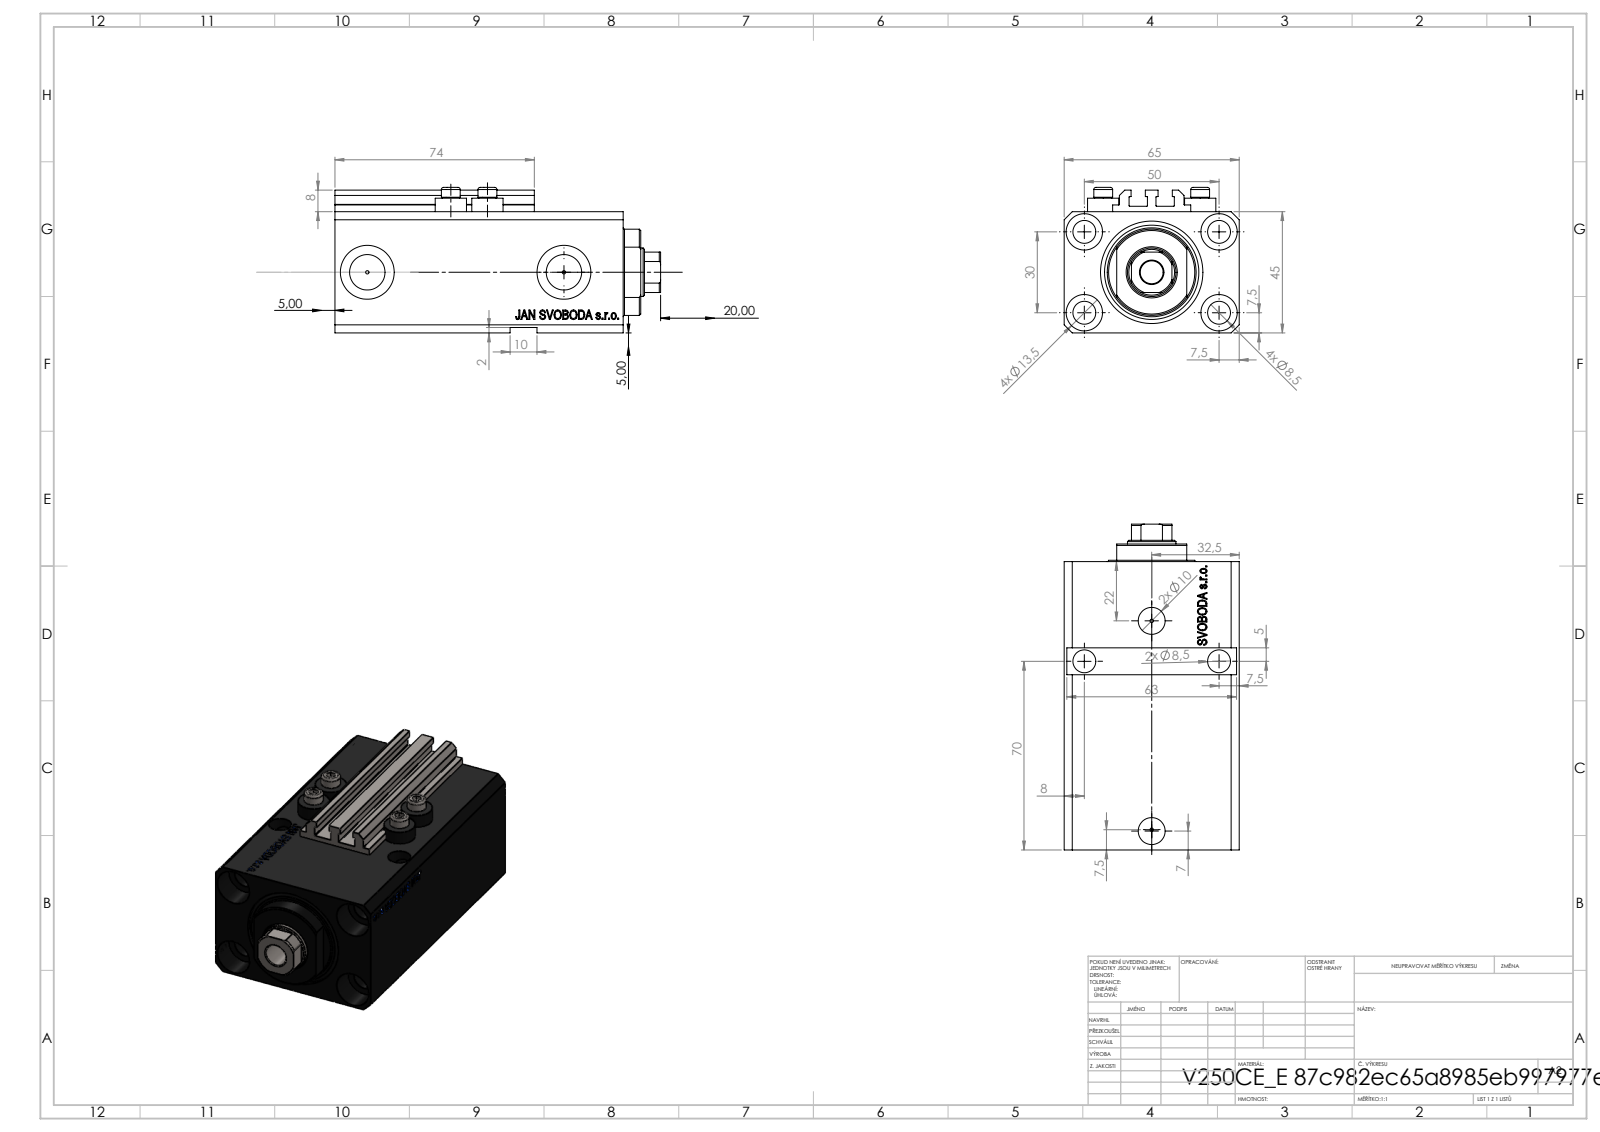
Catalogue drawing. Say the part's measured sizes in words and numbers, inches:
The part is named "V250CE_C_VCP; V250CE_E_Body; ALLEN BOLT V250CE; V250CE_VC_E". Its 3-D file was written by "SolidWorks 2019 (CONFIG_CONTROL_DESIGN)". It is 8 solids with 1087 faces: 511 planar, 146 cylindrical and 430 other. Overall it measures 4.764 by 2.559 by 2.126 inches. Its volume is 16.68 cubic inches and its surface area 119.2 square inches. Round holes: 9 of diameter 0.335, 4 of diameter 0.049, 4 of diameter 0.157, 4 of diameter 0.531, 2 of diameter 0.394, 2 of diameter 0.518, 2 of diameter 0.787, 1 of diameter 0.709, 1 of diameter 0.984, 1 of diameter 1.496. Round bosses or shafts: 4 of diameter 0.457, 4 of diameter 0.276. Partial cylindrical surfaces (rounded edges, fillets, slot ends): 10 of radius 0.008, 1 of radius 0.335, 1 of radius 0.63. The main face-to-face distances are 1.772, 2.559, 3.661, 0.079, 0.551, 1.85, 4.213, 0.098, 0.394, 0.807. The hole center spacings are 1.148, 1.969, 0.535, 0.581, 0.595, 1.083, 1.098, 1.181.
